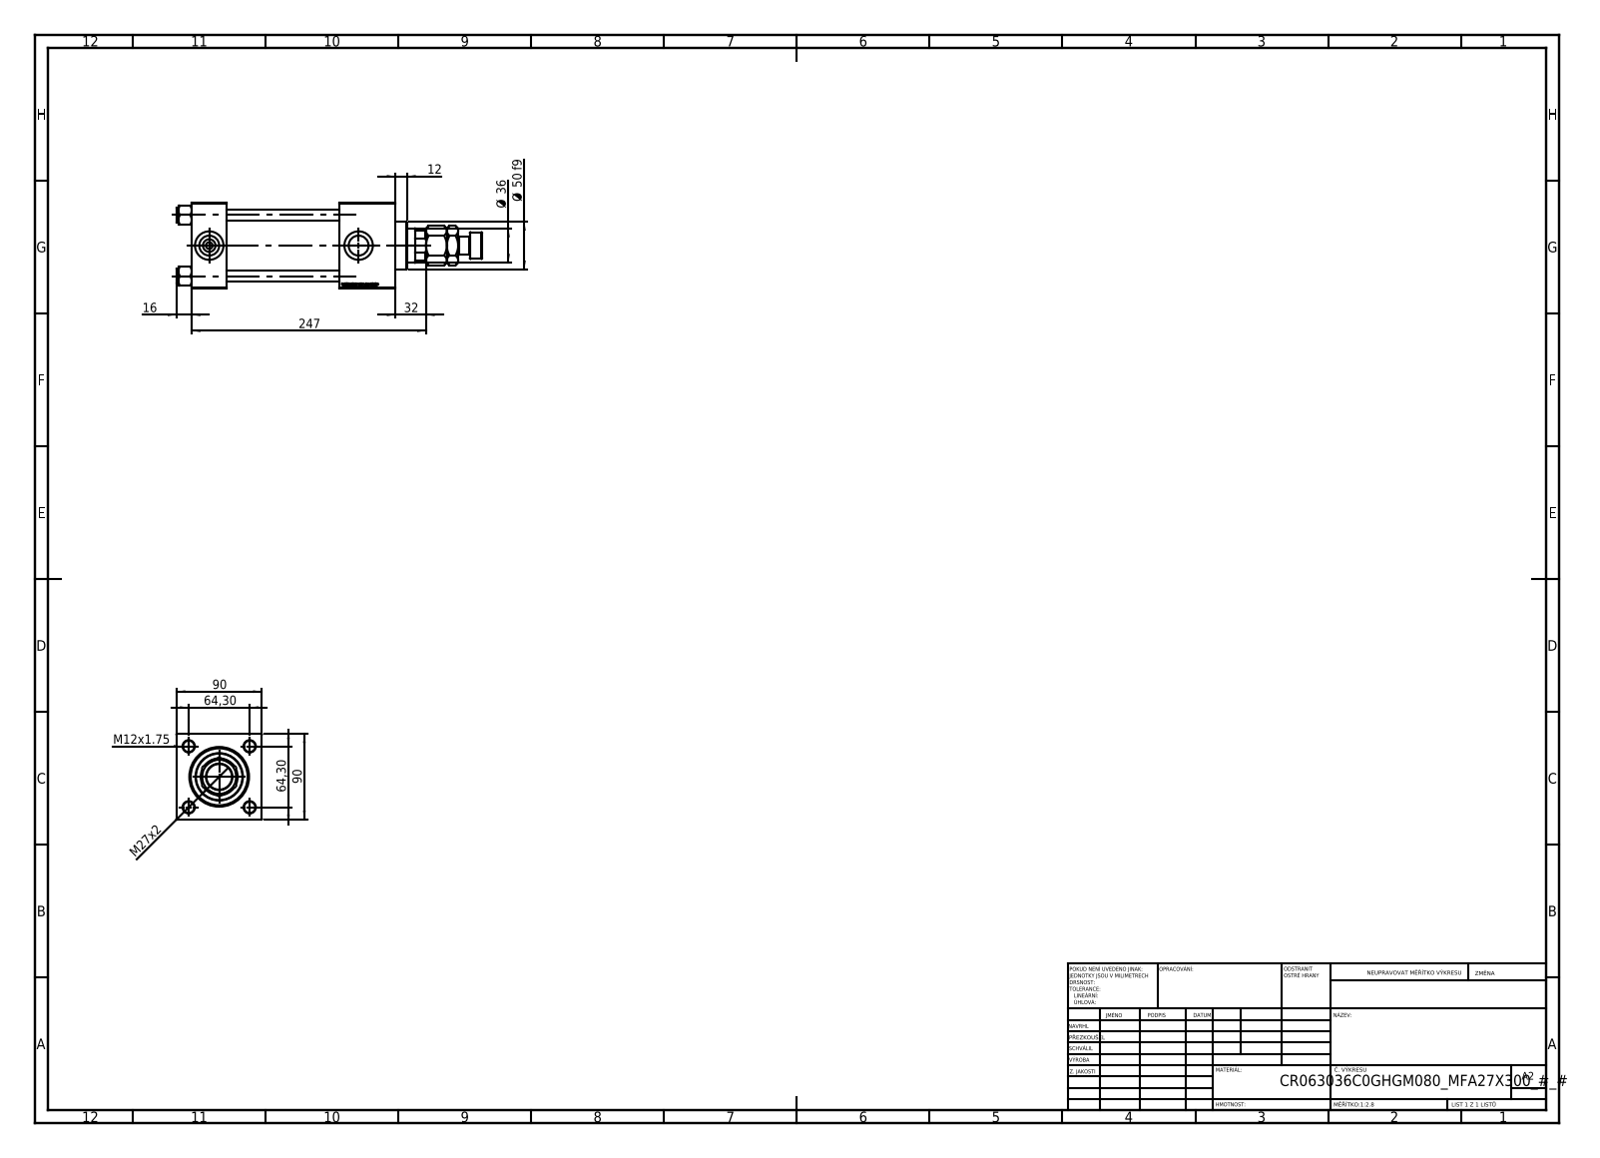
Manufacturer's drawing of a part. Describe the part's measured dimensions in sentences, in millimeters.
The part is named "MFA; V215CR_VCP_C; V215CR_C_TYCINKA; NUT_M5_C (+2 more)". Its 3-D file was written by "SolidWorks 2019 (CONFIG_CONTROL_DESIGN)". It is 12 solids with 1200 faces: 542 planar, 90 cylindrical and 568 other. Overall it measures 322 by 90 by 90 millimeters. Its volume is 1 142 000 cubic millimeters and its surface area 233 744 square millimeters. Round holes: 4 of diameter 12, 2 of diameter 7, 2 of diameter 20.96, 2 of diameter 30, 1 of diameter 25.5, 1 of diameter 36, 1 of diameter 39, 1 of diameter 50, 1 of diameter 60, 1 of diameter 63. Round bosses or shafts: 4 of diameter 15, 1 of diameter 69, 1 of diameter 28, 1 of diameter 18. Partial cylindrical surfaces (rounded edges, fillets, slot ends): 1 of radius 17.5. The main face-to-face distances are 90, 37, 59, 215, 178, 156, 119, 186.3, 149.3, 30.3. The hole center spacings are 45.47, 64.3, 90.93, 157.5.
